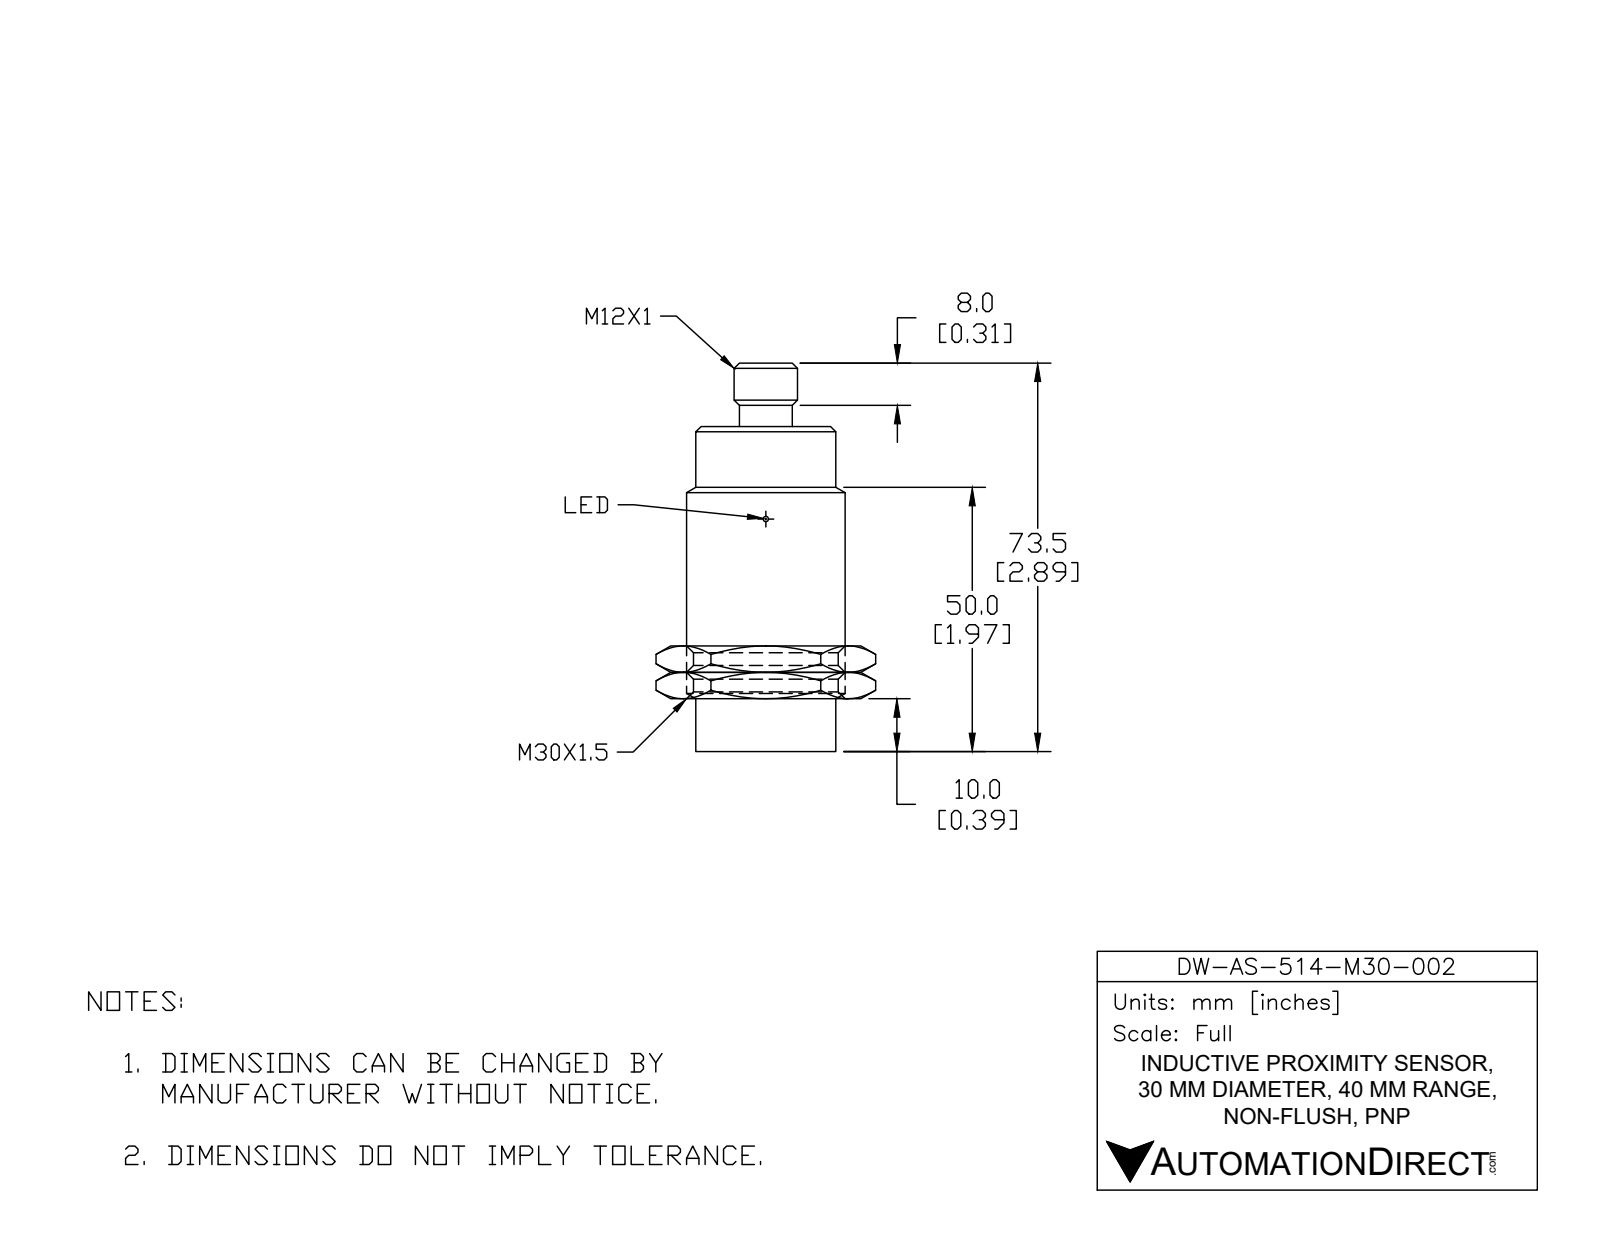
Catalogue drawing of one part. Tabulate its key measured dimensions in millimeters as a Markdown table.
| quantity | value |
| --- | --- |
| part name | DW-AS-514-M30-002 |
| STEP written by | SolidWorks 2017 (AUTOMOTIVE_DESIGN) |
| units | millimeters |
| bodies | 1 solid, 36 faces (13 planar, 14 cylindrical, 9 other) |
| overall size | 73.6 × 30 × 30 |
| volume | 41 480 mm³ |
| surface area | 7 806 mm² |
| round holes (diameter × count) | 3 × 2, 8.5 × 1 |
| round bosses / shafts (diameter × count) | 1.1 × 3, 30 × 1, 27.8 × 1, 27.5 × 1, 12 × 1, 10.5 × 1 |
| partial cylindrical surfaces (radius × count) | 0.5 × 2, 0.6 × 1 |
| main face-to-face distances | 60.5, 64.8, 4.3, 52, 8.5, 12.9, 10, 42, 50.5, 54.8 |
